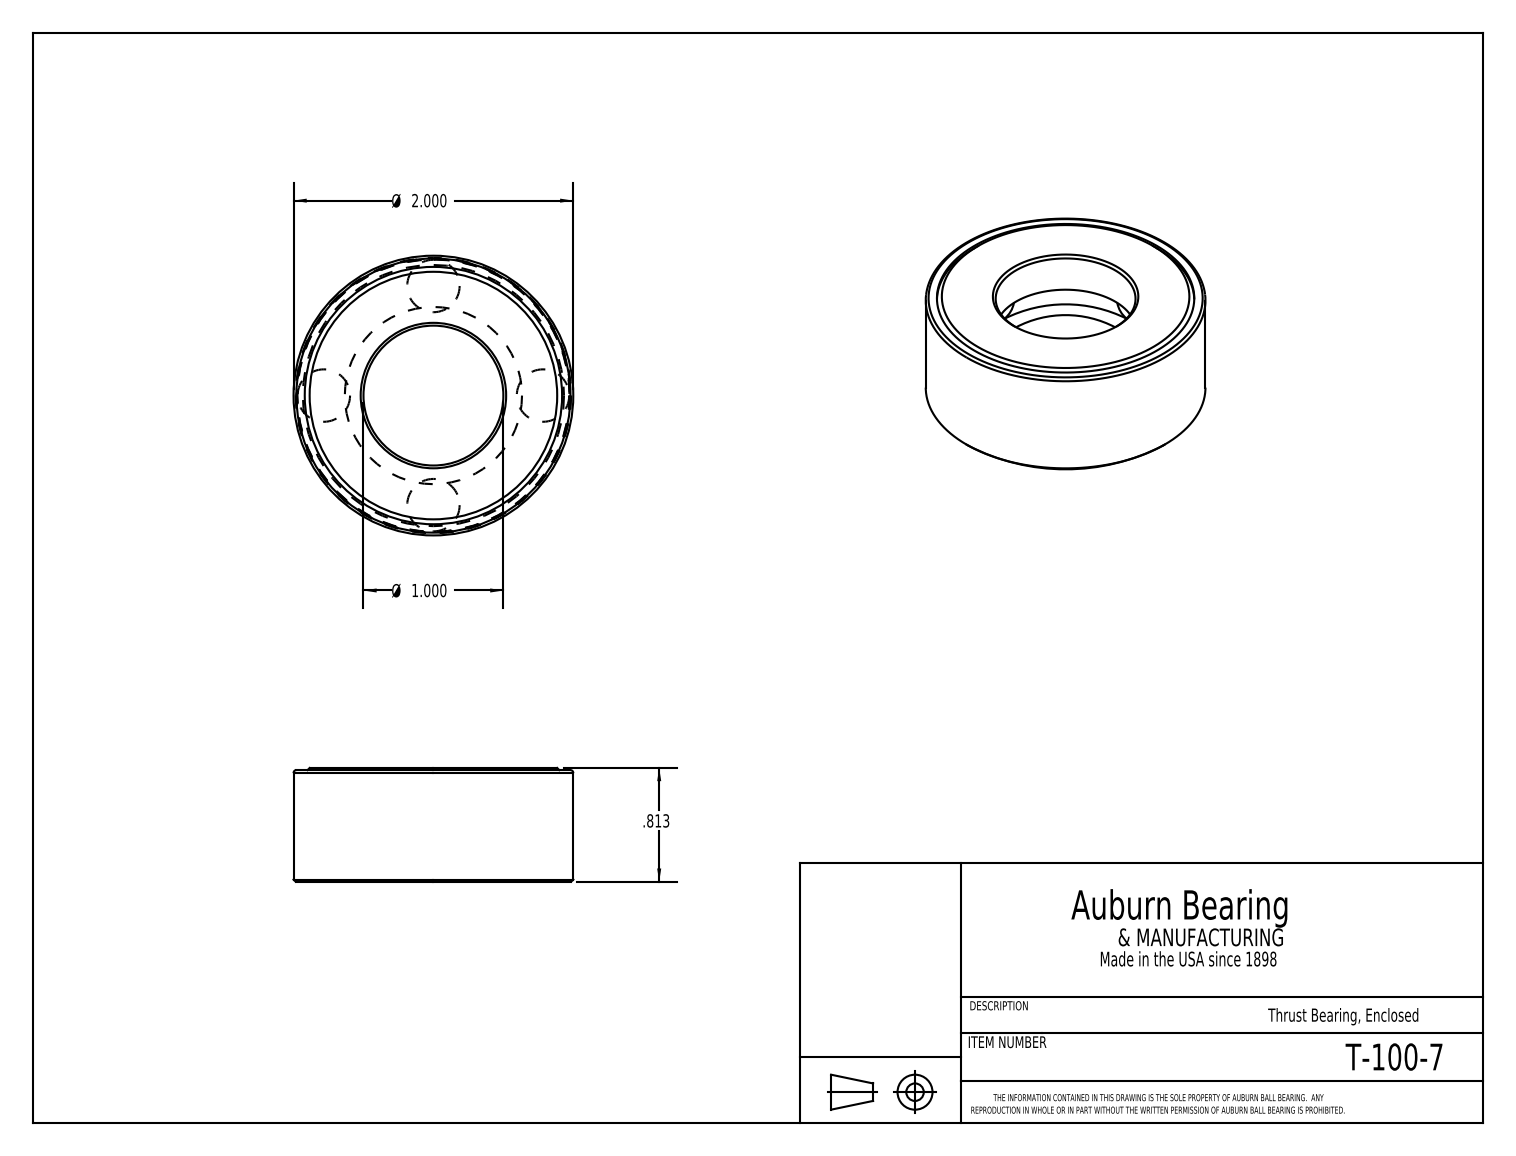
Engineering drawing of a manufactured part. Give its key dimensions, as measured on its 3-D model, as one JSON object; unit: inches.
{"part_name": "T-100-7", "step_written_by": "SolidWorks 2016 (CONFIG_CONTROL_DESIGN)", "units": "inches", "bodies": {"solids": 6, "faces": 28, "planar": 9, "cylindrical": 7, "other": 12}, "overall_size": [2, 2, 0.813], "volume_in3": 1.335, "surface_area_in2": 23.33, "round_holes": [[1, 1], [1.84, 1], [1.96, 1]], "round_bosses_or_shafts": [[2, 1], [1.946, 1]], "face_to_face_distances": [0.813, 0.294, 0.519, 0.225, 0.778, 0.484, 0.259, 0.035, 0.798, 0.504]}
